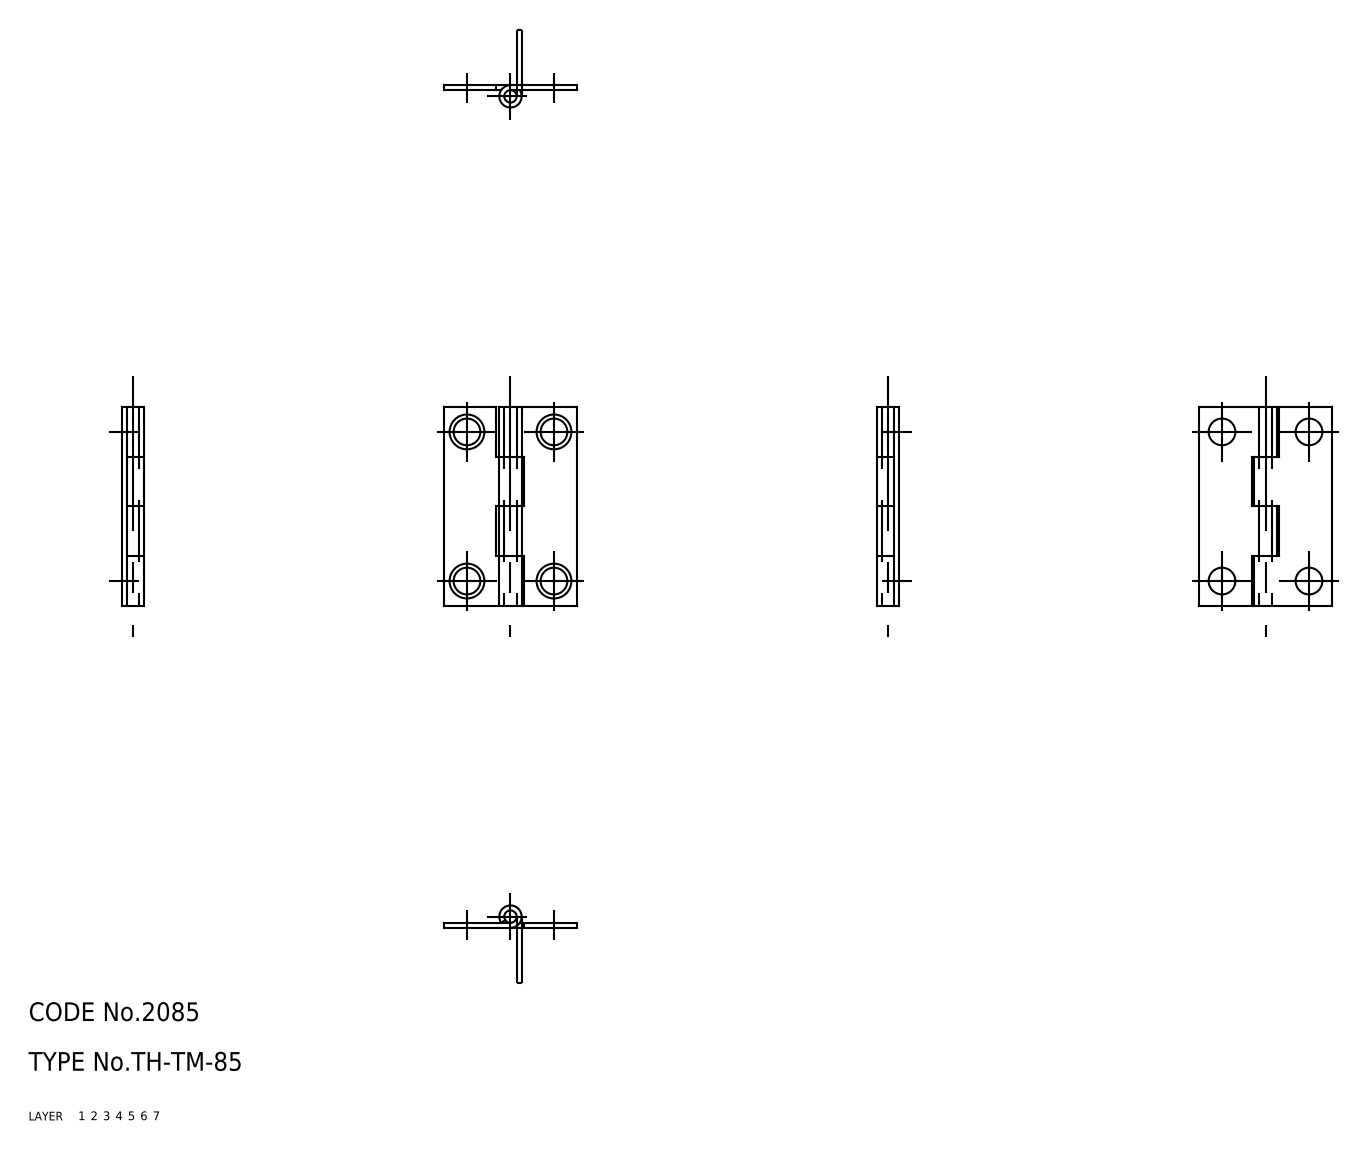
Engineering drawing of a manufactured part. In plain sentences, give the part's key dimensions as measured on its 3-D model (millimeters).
The part is named "shaft; hinge piece_B; hinge piece_A; TH_TM_85_26128_36". Its 3-D file was written by "CADfix (AUTOMOTIVE_DESIGN)". It is 3 solids with 52 faces: 0 planar, 0 cylindrical and 52 other. Overall it measures 32 by 21.5 by 3.6 millimeters. Its volume is 723 cubic millimeters and its surface area 2 012 square millimeters.
